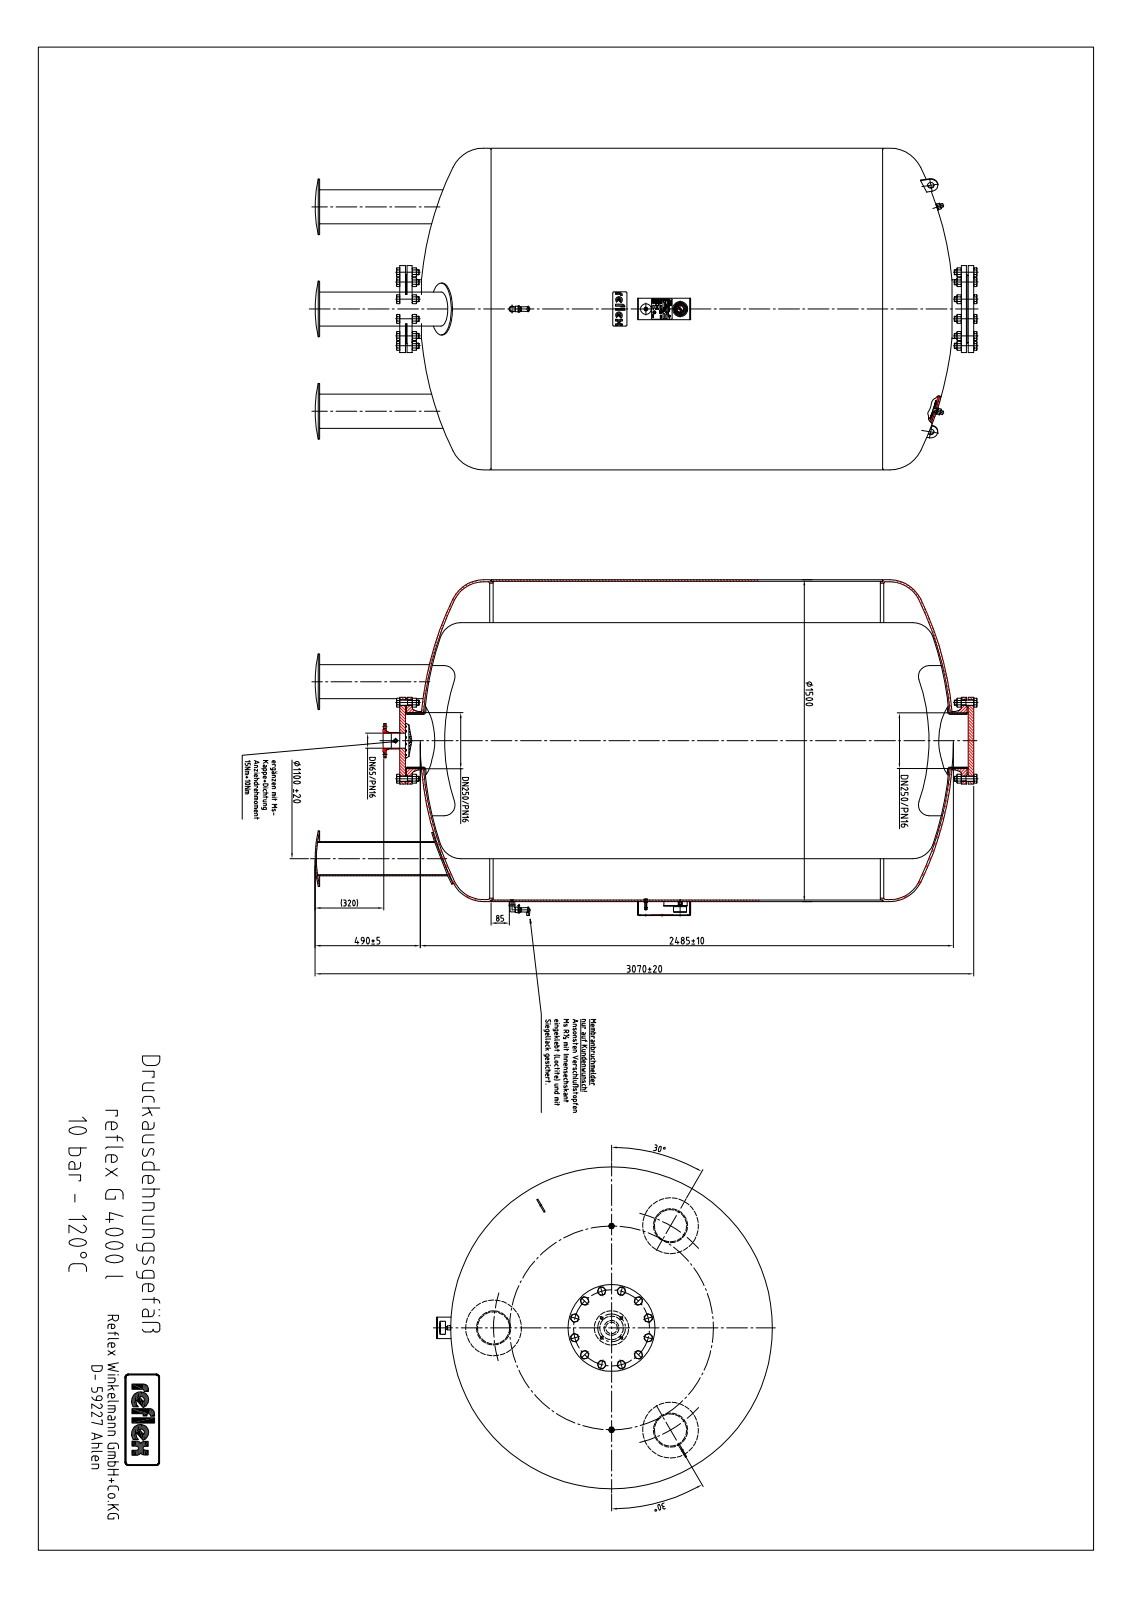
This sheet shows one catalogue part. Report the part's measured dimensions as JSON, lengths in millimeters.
{"step_written_by": "Mechanical Desktop 2008 (CONFIG_CONTROL_DESIGN)", "units": "millimeters", "bodies": {"solids": 20, "faces": 817, "planar": 473, "cylindrical": 190, "other": 154}, "overall_size": [3080, 1566, 1502.44], "volume_mm3": 4082000000, "surface_area_mm2": 23300000, "round_holes": [[10, 1], [30, 1], [50, 1], [69, 1], [260.4, 1]], "round_bosses_or_shafts": [[16, 12], [159, 3], [28, 2], [26, 2], [20, 2], [1500, 1], [405, 1], [273, 1]], "partial_cylinders_radius": [[8.44, 4], [3.38, 3], [1, 2], [5, 2], [5.76, 2], [10, 2], [10.12, 2], [13.91, 2]], "face_to_face_distances": [1825, 26, 2638, 31, 2607, 57, 2581, 388, 2213, 2612], "hole_center_spacings": [82.33, 765.5]}
